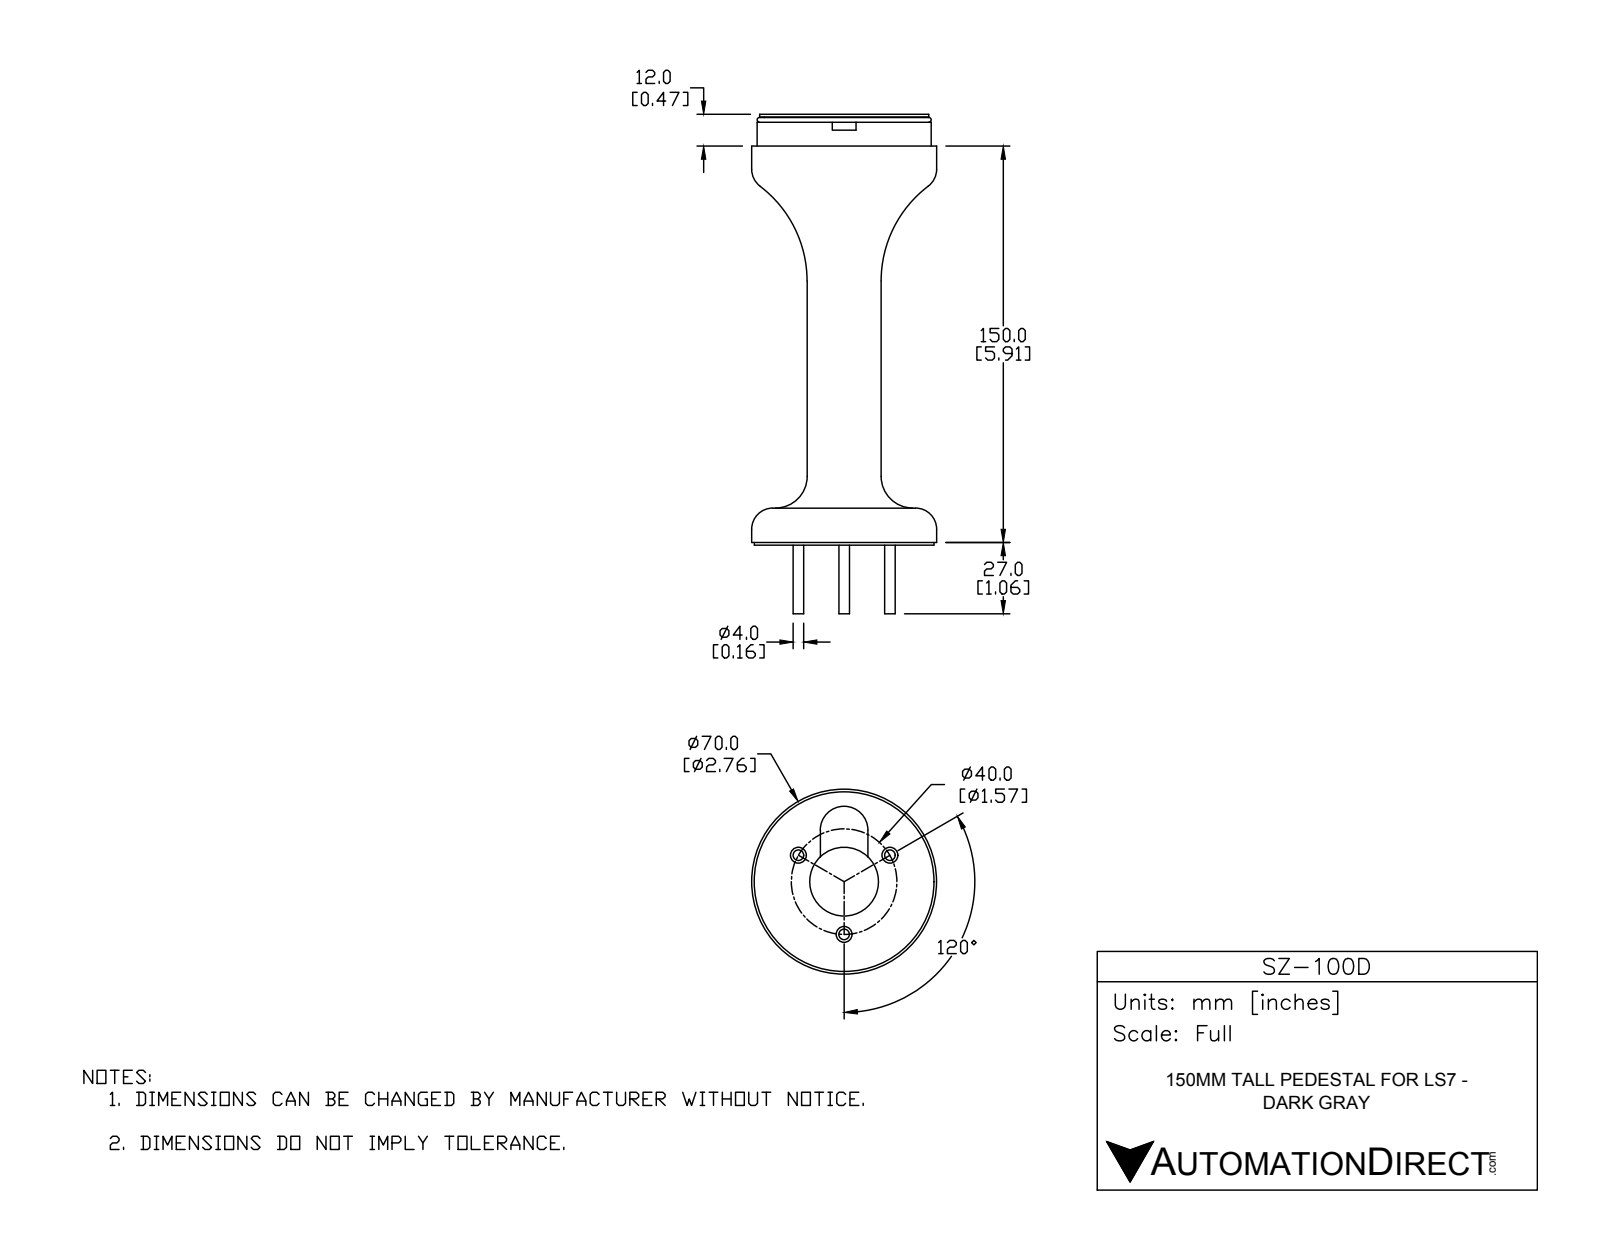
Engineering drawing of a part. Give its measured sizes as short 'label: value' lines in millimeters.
name: SZ-100D
written by: SolidWorks 2016 (AUTOMOTIVE_DESIGN)
unit: mm
bodies: 6 solids, 88 faces (31 planar, 35 cylindrical, 22 other)
size: 189 × 70 × 70
volume: 93 150 mm³; area: 54 497 mm²
holes: 3× ⌀6, 1× ⌀26, 1× ⌀60
bosses: 3× ⌀4, 1× ⌀70, 1× ⌀68, 1× ⌀65.9, 1× ⌀64, 1× ⌀60.4, 1× ⌀28
rounds: 1× R1, 1× R9
face distances: 1, 162, 160, 159, 9, 151, 150, 3, 163, 12
hole spacings: 20, 34.64
